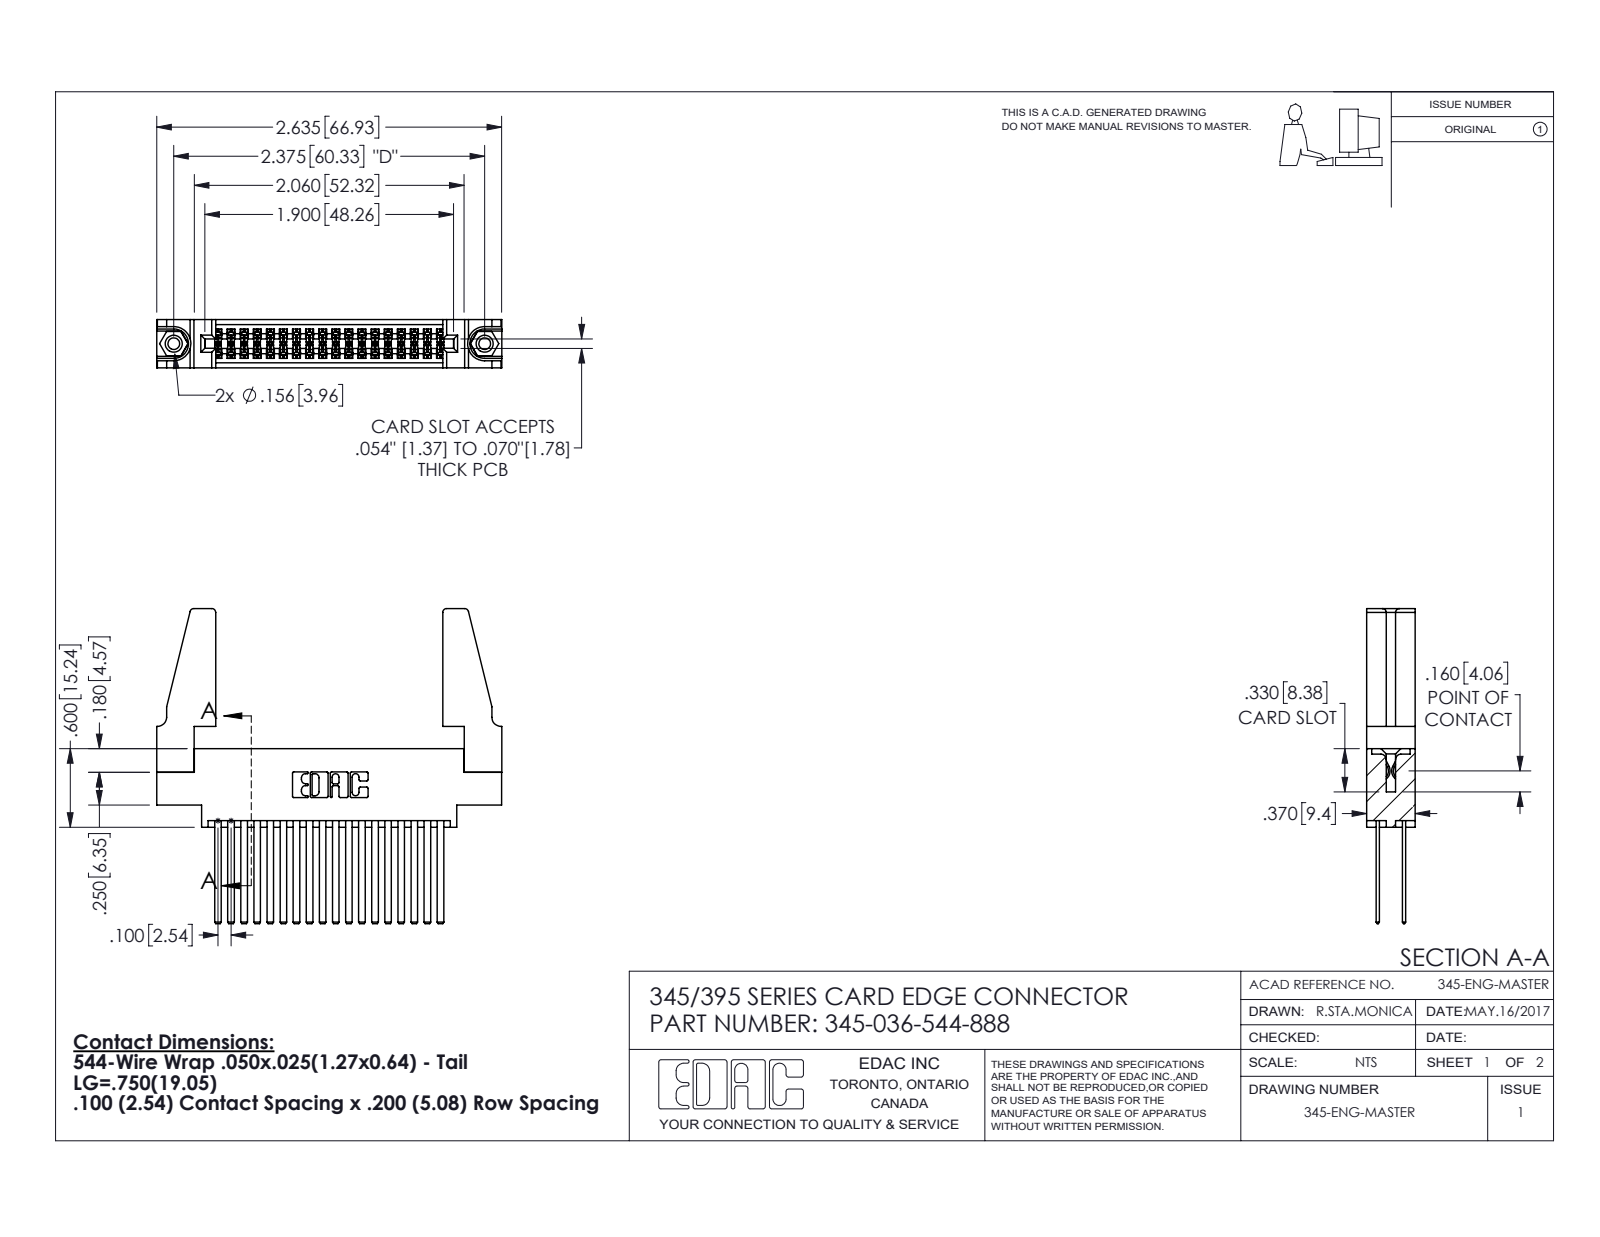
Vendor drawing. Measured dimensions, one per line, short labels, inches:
name: 345 Part_0.170 Offset - 0.156 Dia-TH; 345-250-001_345-250-001-102; 345-036-544-888; 345-292-001_345-293-144 (+1 more)
written by: SolidWorks 2016 (CONFIG_CONTROL_DESIGN)
unit: in
bodies: 41 solids, 1838 faces (1200 planar, 622 cylindrical, 16 other)
size: 2.636 × 2.407 × 0.37
volume: 0.606 in³; area: 21.92 in²
holes: 2× ⌀0.089, 2× ⌀0.125, 2× ⌀0.156, 1× ⌀0.064
bosses: 2× ⌀0.155
rounds: 54× R0.006, 22× R0.01, 8× R0.03, 6× R0.007, 6× R0.031, 3× R0.026, 2× R0.014, 2× R0.019
face distances: 0.072, 0.298, 0.2, 0.098, 0.272, 0.025, 0.37, 0.225, 0.175, 0.15
hole spacings: 0.27, 2.141, 2.375
